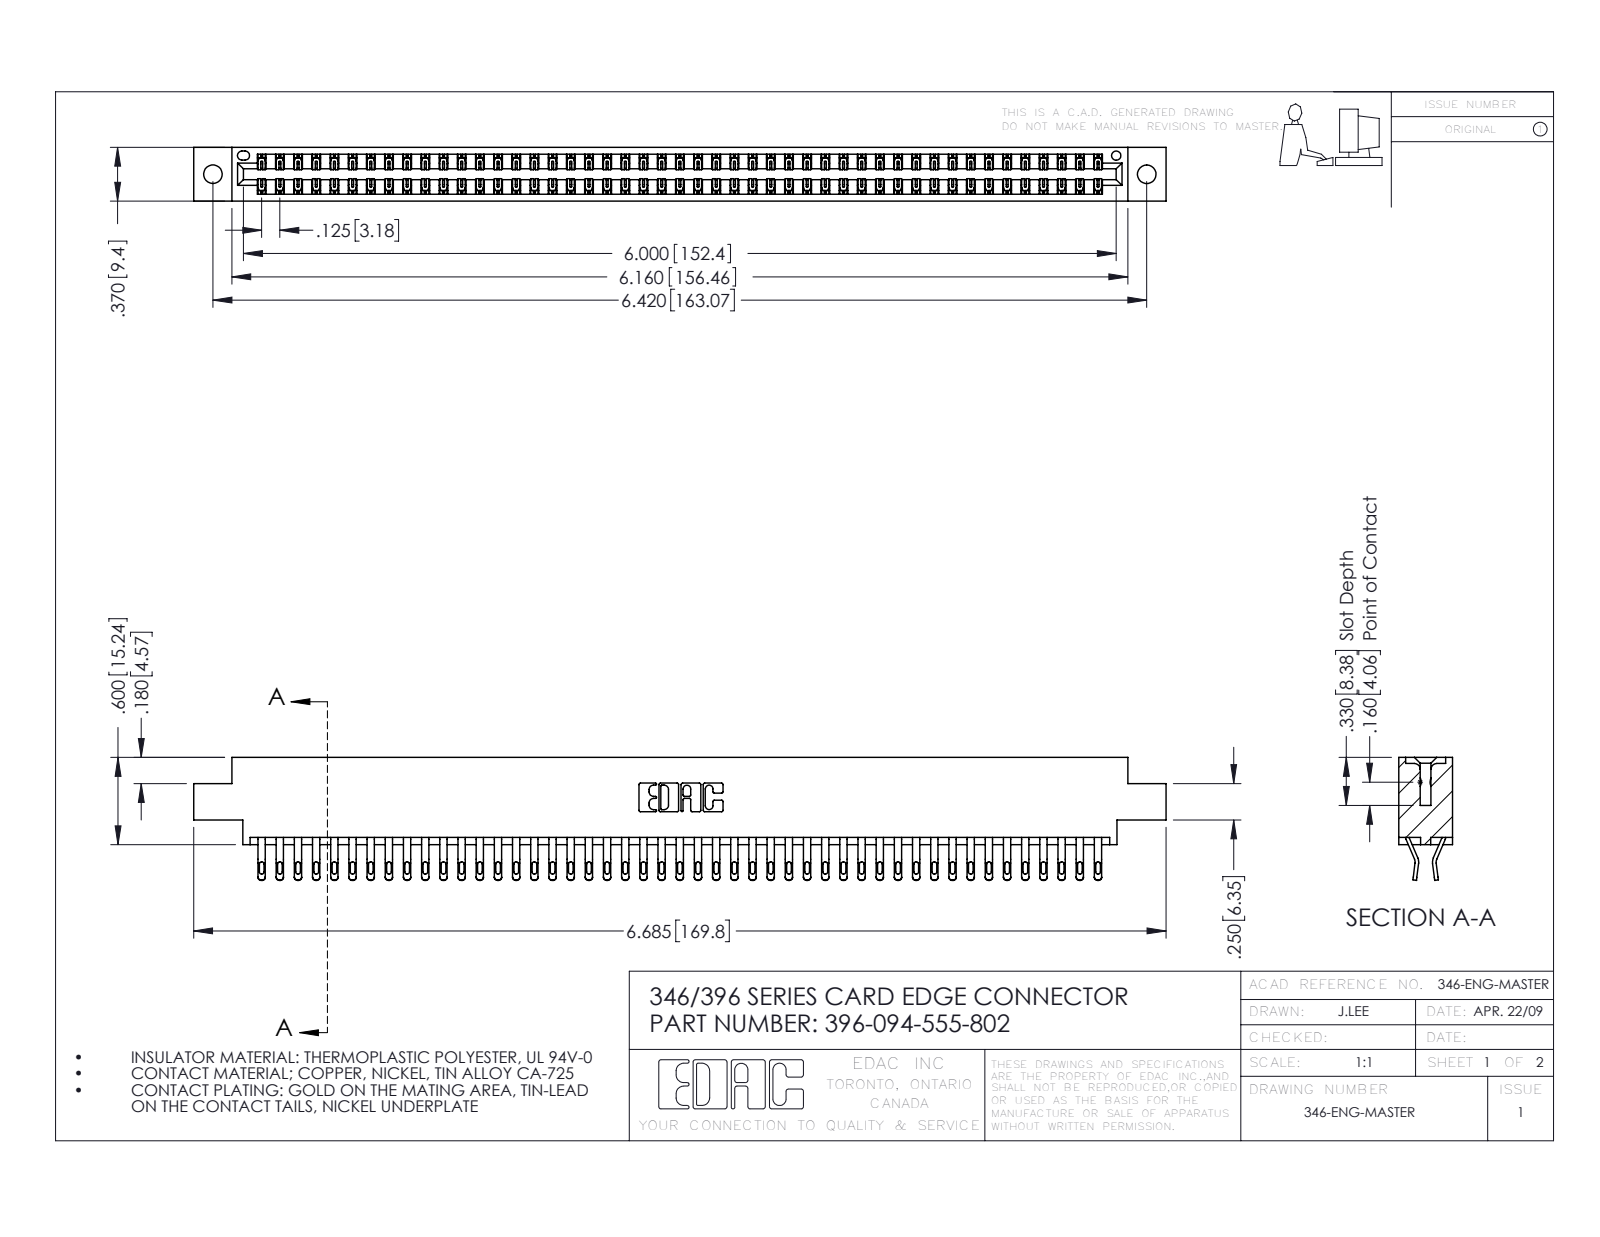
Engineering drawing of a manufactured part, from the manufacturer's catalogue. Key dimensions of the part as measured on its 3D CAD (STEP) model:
Part name (STEP PRODUCT): 396-094-555-802; 346 Part_0.170 Offset - 0.128 Dia; 345-292-001_555 Tail
STEP written by: SolidWorks 2016 (CONFIG_CONTROL_DESIGN)
Units: inches
Bodies: 95 solids, 5578 faces (3182 planar, 2396 cylindrical, 0 other)
Overall size (bounding box): 6.685 × 0.845 × 0.37
Volume: 1.018 in³ · Surface area: 37.02 in²
Round holes (diameter × count): ⌀0.128 ×2, ⌀0.064 ×1
Partial cylindrical surfaces — rounded edges, fillets, slot ends (radius × count): R0.016 ×188, R0.02 ×188, R0.006 ×141, R0.01 ×22, R0.007 ×6, R0.031 ×6, R0.026 ×3, R0.01 ×2
Main face-to-face distances: 0.048, 0.322, 0.37, 0.25, 0.025, 0.072, 0.298, 0.275, 0.148, 0.222
Hole centre spacings: 0.246, 6.211, 6.42
